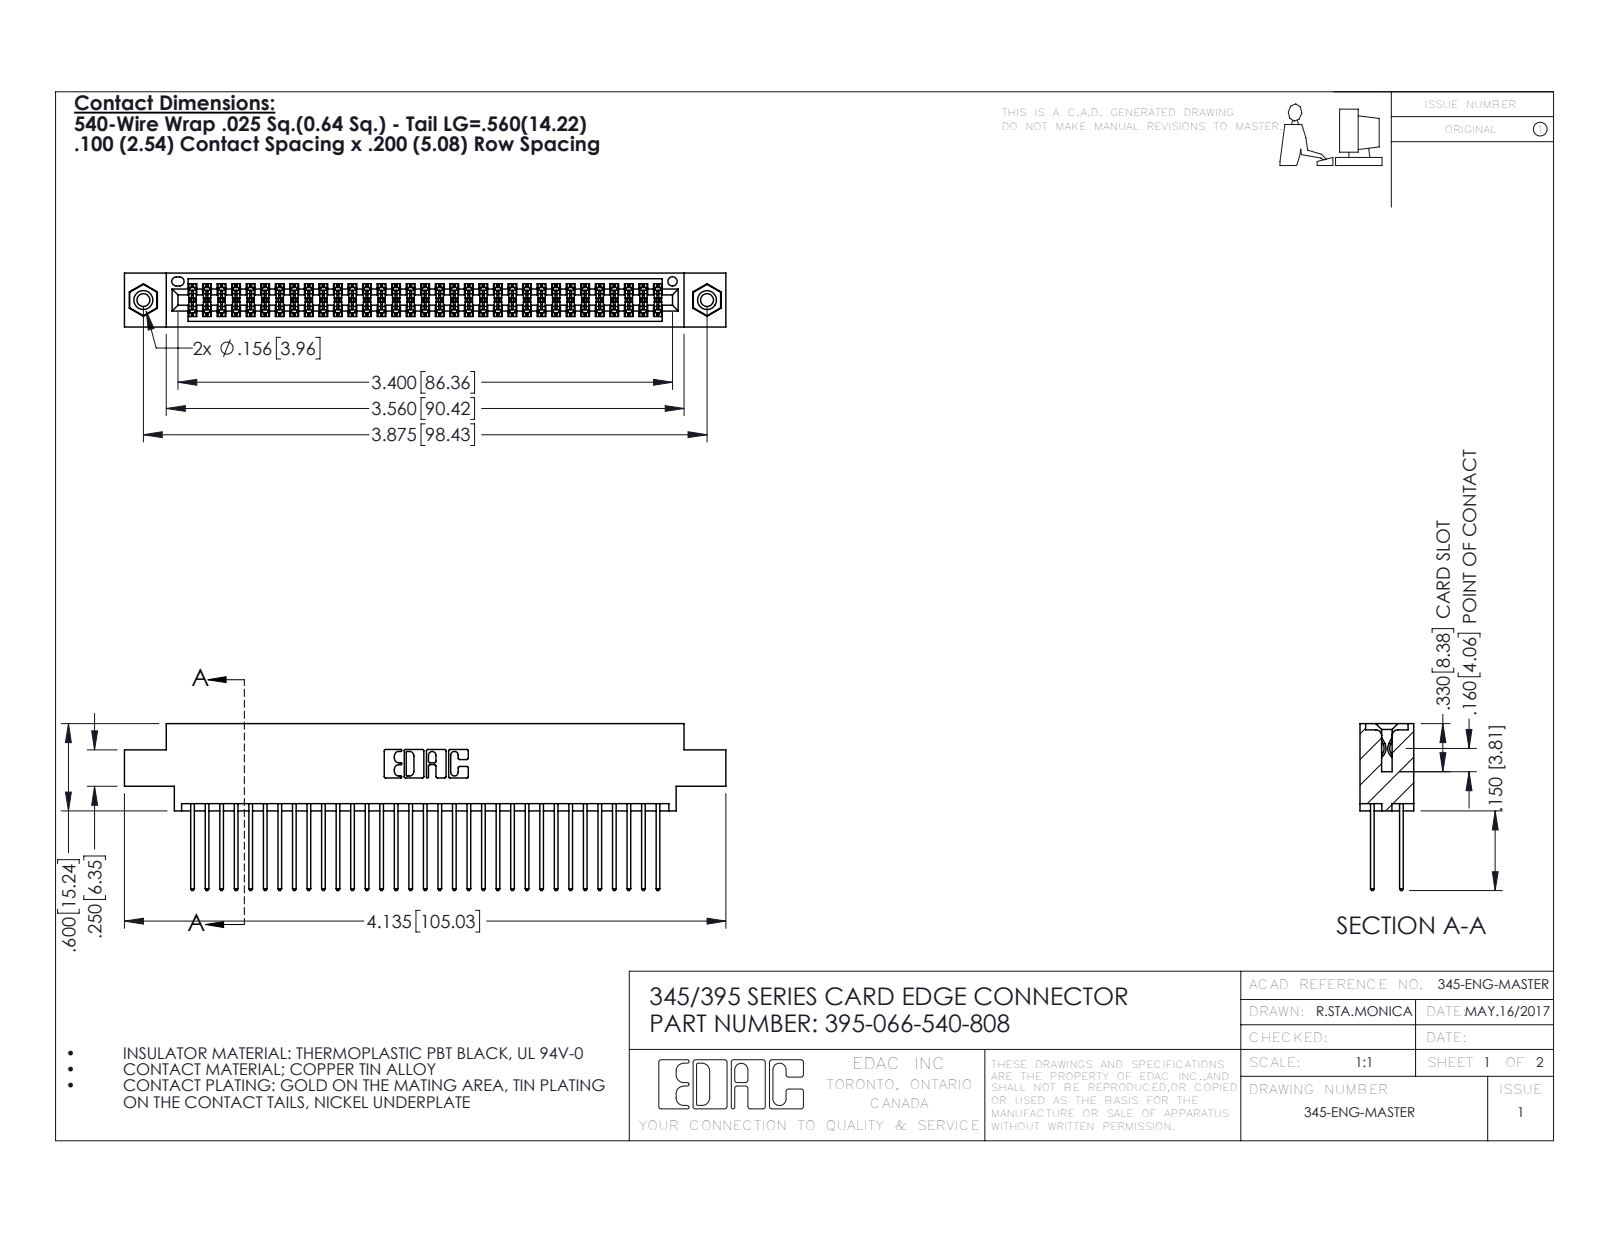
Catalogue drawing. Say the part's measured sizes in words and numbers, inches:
The part is named "345-250-001_345-250-003-102; 345 Part_0.170 Offset - 0.156 Dia-TI; 345-292-001_345-293-140; 395-066-540-808". Its 3-D file was written by "SolidWorks 2016 (CONFIG_CONTROL_DESIGN)". It is 69 solids with 3490 faces: 2294 planar, 1180 cylindrical and 16 other. Overall it measures 4.135 by 1.147 by 0.37 inches. Its volume is 0.625 cubic inches and its surface area 25.26 square inches. Round holes: 2 of diameter 0.089, 2 of diameter 0.125, 2 of diameter 0.156, 1 of diameter 0.064. Round bosses or shafts: 2 of diameter 0.155. Partial cylindrical surfaces (rounded edges, fillets, slot ends): 99 of radius 0.006, 66 of radius 0.01, 22 of radius 0.01, 6 of radius 0.007, 6 of radius 0.031, 3 of radius 0.026, 2 of radius 0.014, 2 of radius 0.019. The main face-to-face distances are 0.072, 0.298, 0.2, 0.098, 0.272, 0.025, 0.37, 0.225, 0.175, 0.149. The hole center spacings are 0.27, 3.64, 3.875.
